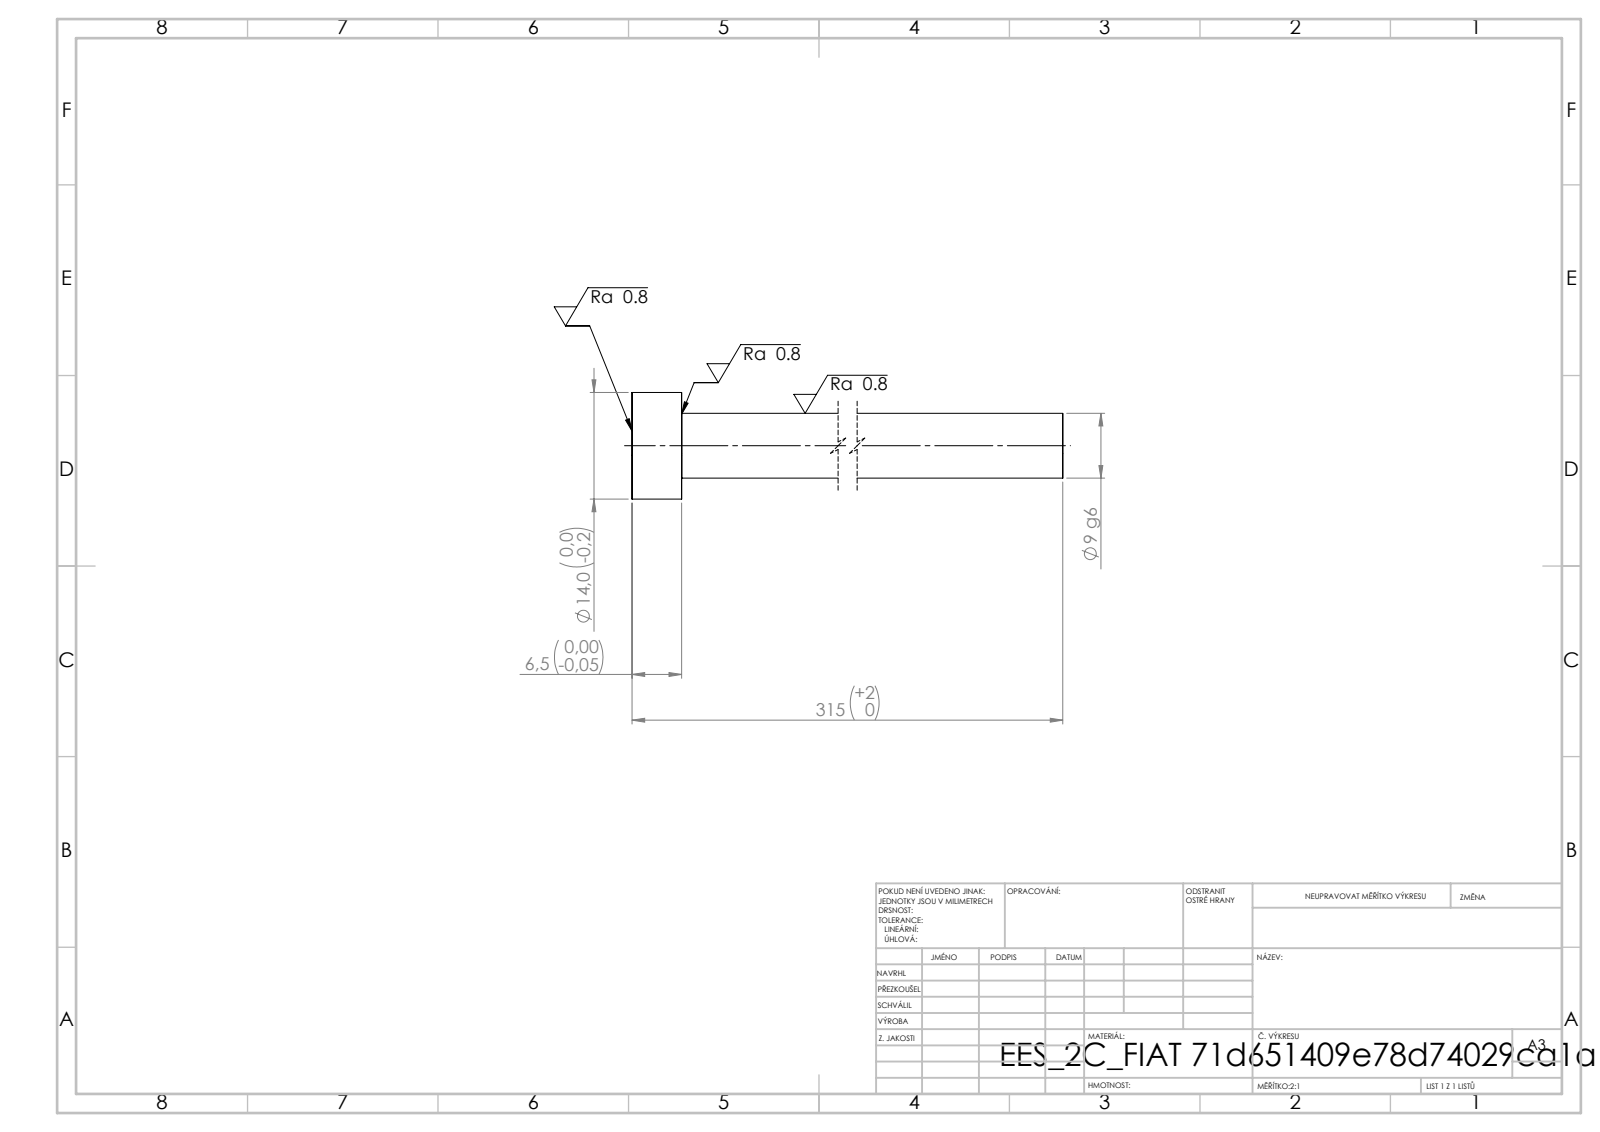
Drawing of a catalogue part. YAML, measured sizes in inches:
step_written_by: "SolidWorks 2019 (CONFIG_CONTROL_DESIGN)"
units: inches
bodies: {solids: 1, faces: 7, planar: 3, cylindrical: 4, other: 0}
overall_size: [12.402, 0.551, 0.551]
volume: 1.129
surface_area: 13.69
round_bosses_or_shafts:
  - {diameter: 0.551, count: 1}
  - {diameter: 0.335, count: 1}
face_to_face_distances: [0.256, 12.402, 12.146]
